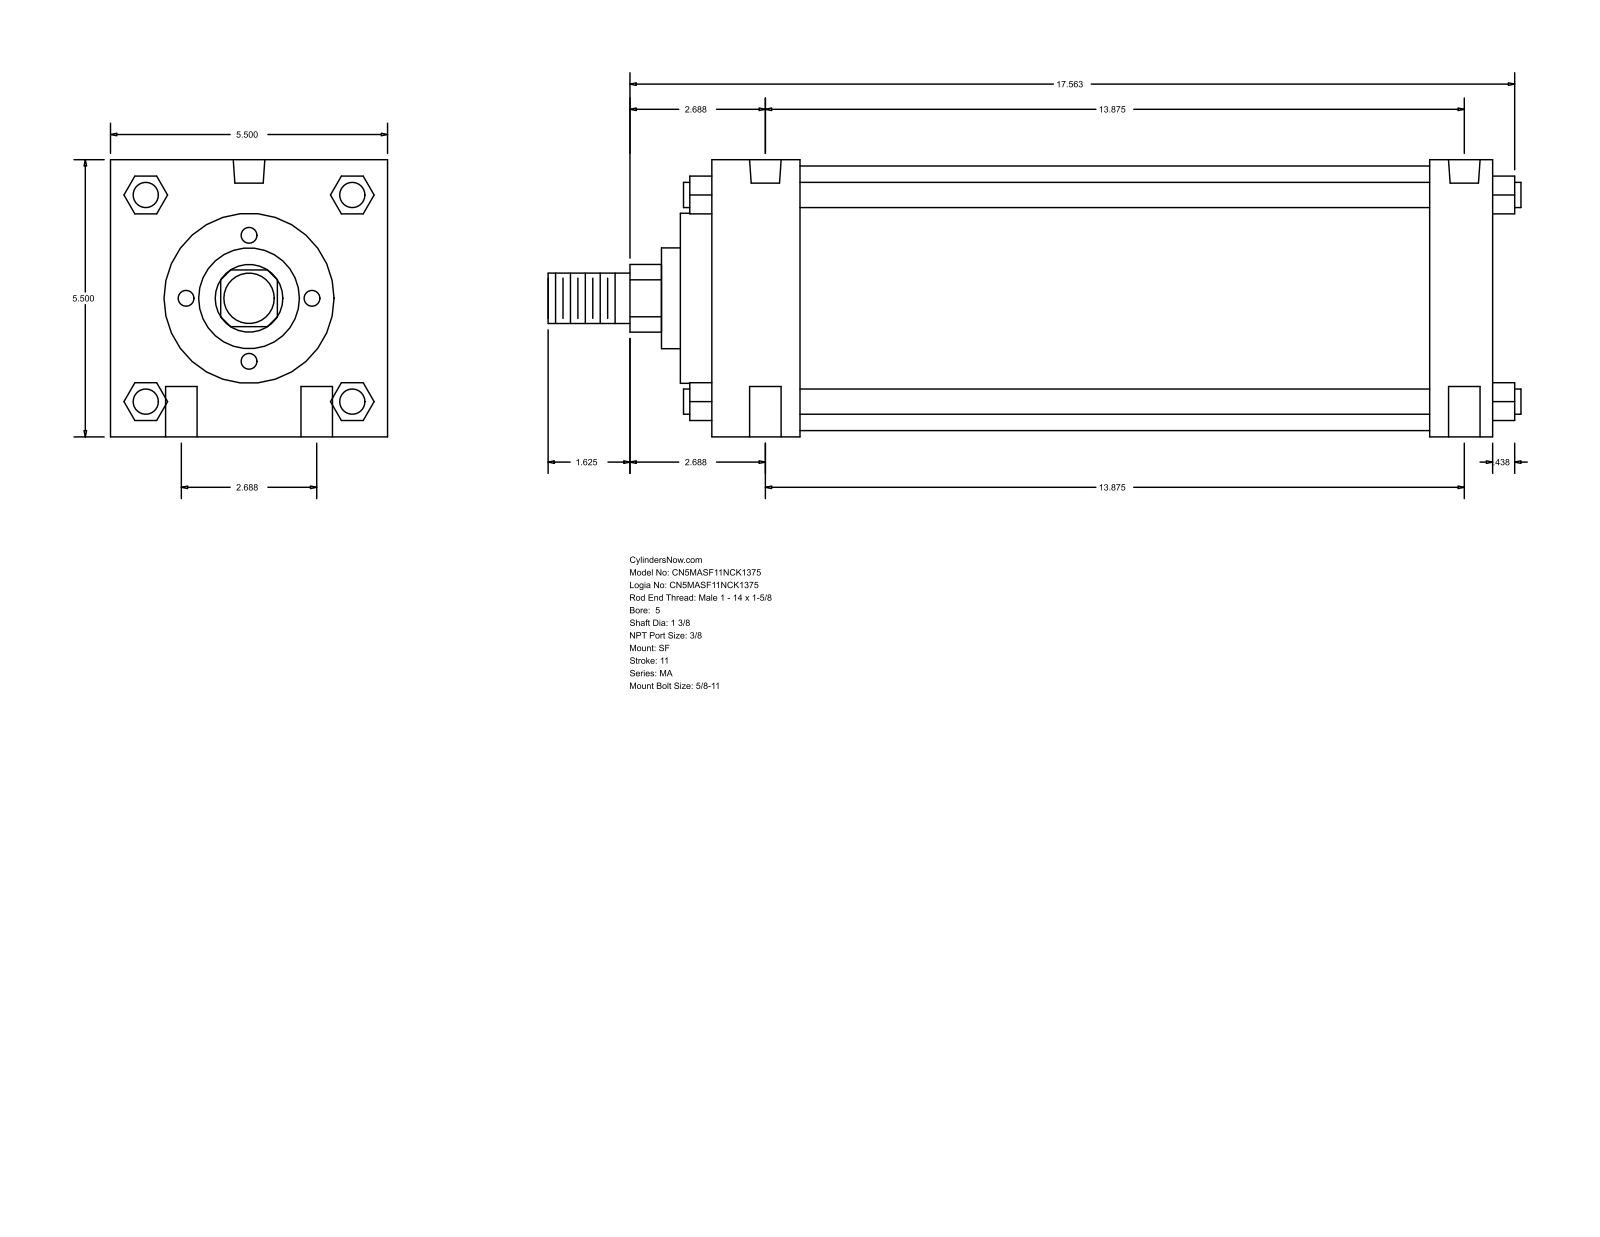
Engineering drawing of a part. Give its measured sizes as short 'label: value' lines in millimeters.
name: MA_SF__0500_1.375
written by: GSSL Pune (CONFIG_CONTROL_DESIGN)
unit: mm
bodies: 0 solids, 126 faces (95 planar, 31 cylindrical, 0 other)
size: 490.54 × 139.7 × 139.7
holes: 4× ⌀15.88, 2× ⌀11.11, 2× ⌀15.93
bosses: 4× ⌀12.7, 1× ⌀133.35, 1× ⌀85.72, 1× ⌀50.8, 1× ⌀34.92, 1× ⌀25.4
rounds: 1× R17.06
face distances: 139.7, 393.71, 44.45, 361.96, 317.51, 349.26, 31.75, 15.87, 60.32, 377.83
hole spacings: 34.13, 354.08, 352.43, 68.26, 358.98, 342.9
